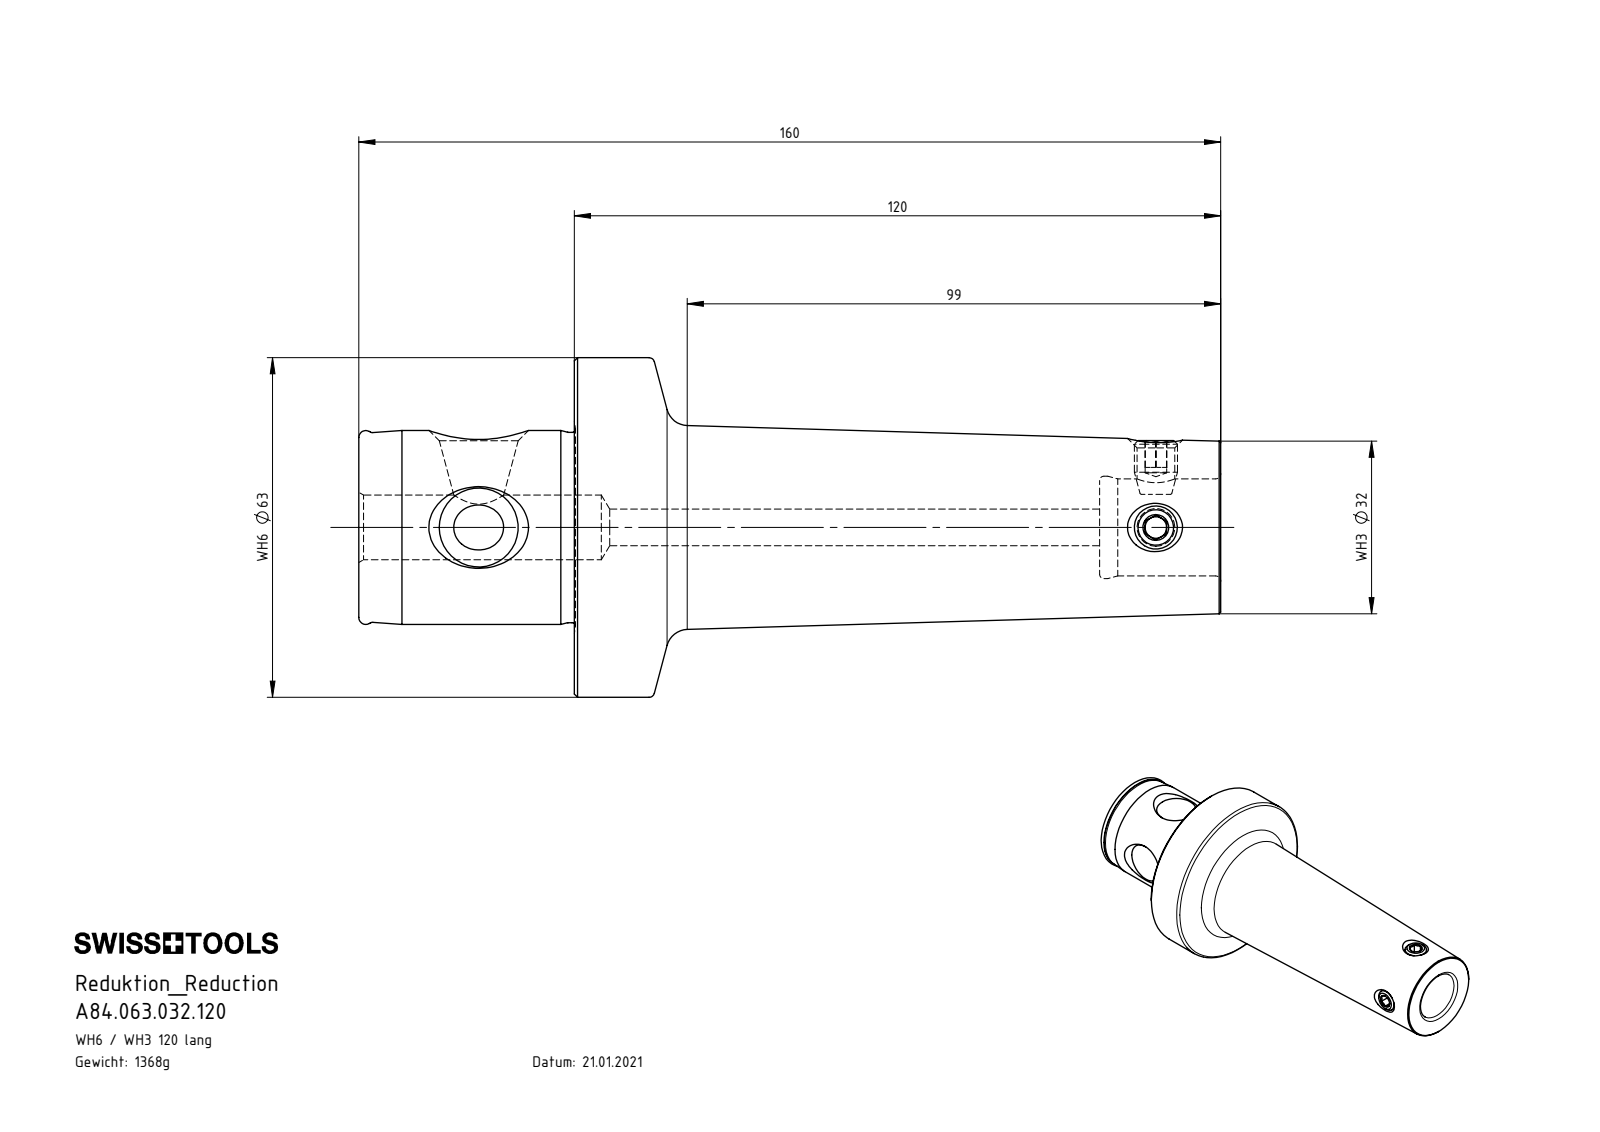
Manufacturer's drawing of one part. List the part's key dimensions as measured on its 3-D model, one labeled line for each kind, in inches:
Part name (STEP PRODUCT): A84.063.032.120; WH6-WH3.K01.120_B; WH3-ER1.001.010
STEP written by: SolidWorks 2017 (CONFIG_CONTROL_DESIGN)
Units: inches
Bodies: 3 solids, 132 faces (32 planar, 26 cylindrical, 74 other)
Overall size (bounding box): 6.299 × 2.48 × 2.48
Volume: 10.64 in³ · Surface area: 47.28 in²
Round holes (diameter × count): ⌀0.157 ×2, ⌀0.276 ×2, ⌀0.268 ×1, ⌀0.472 ×1, ⌀0.709 ×1, ⌀0.748 ×1
Round bosses / shafts (diameter × count): ⌀0.315 ×2, ⌀2.48 ×1, ⌀1.417 ×1, ⌀1.39 ×1
Main face-to-face distances: 1.575, 6.299, 4.724, 5.413, 3.839, 0.886, 0.157, 0.394, 0.158, 0.197
